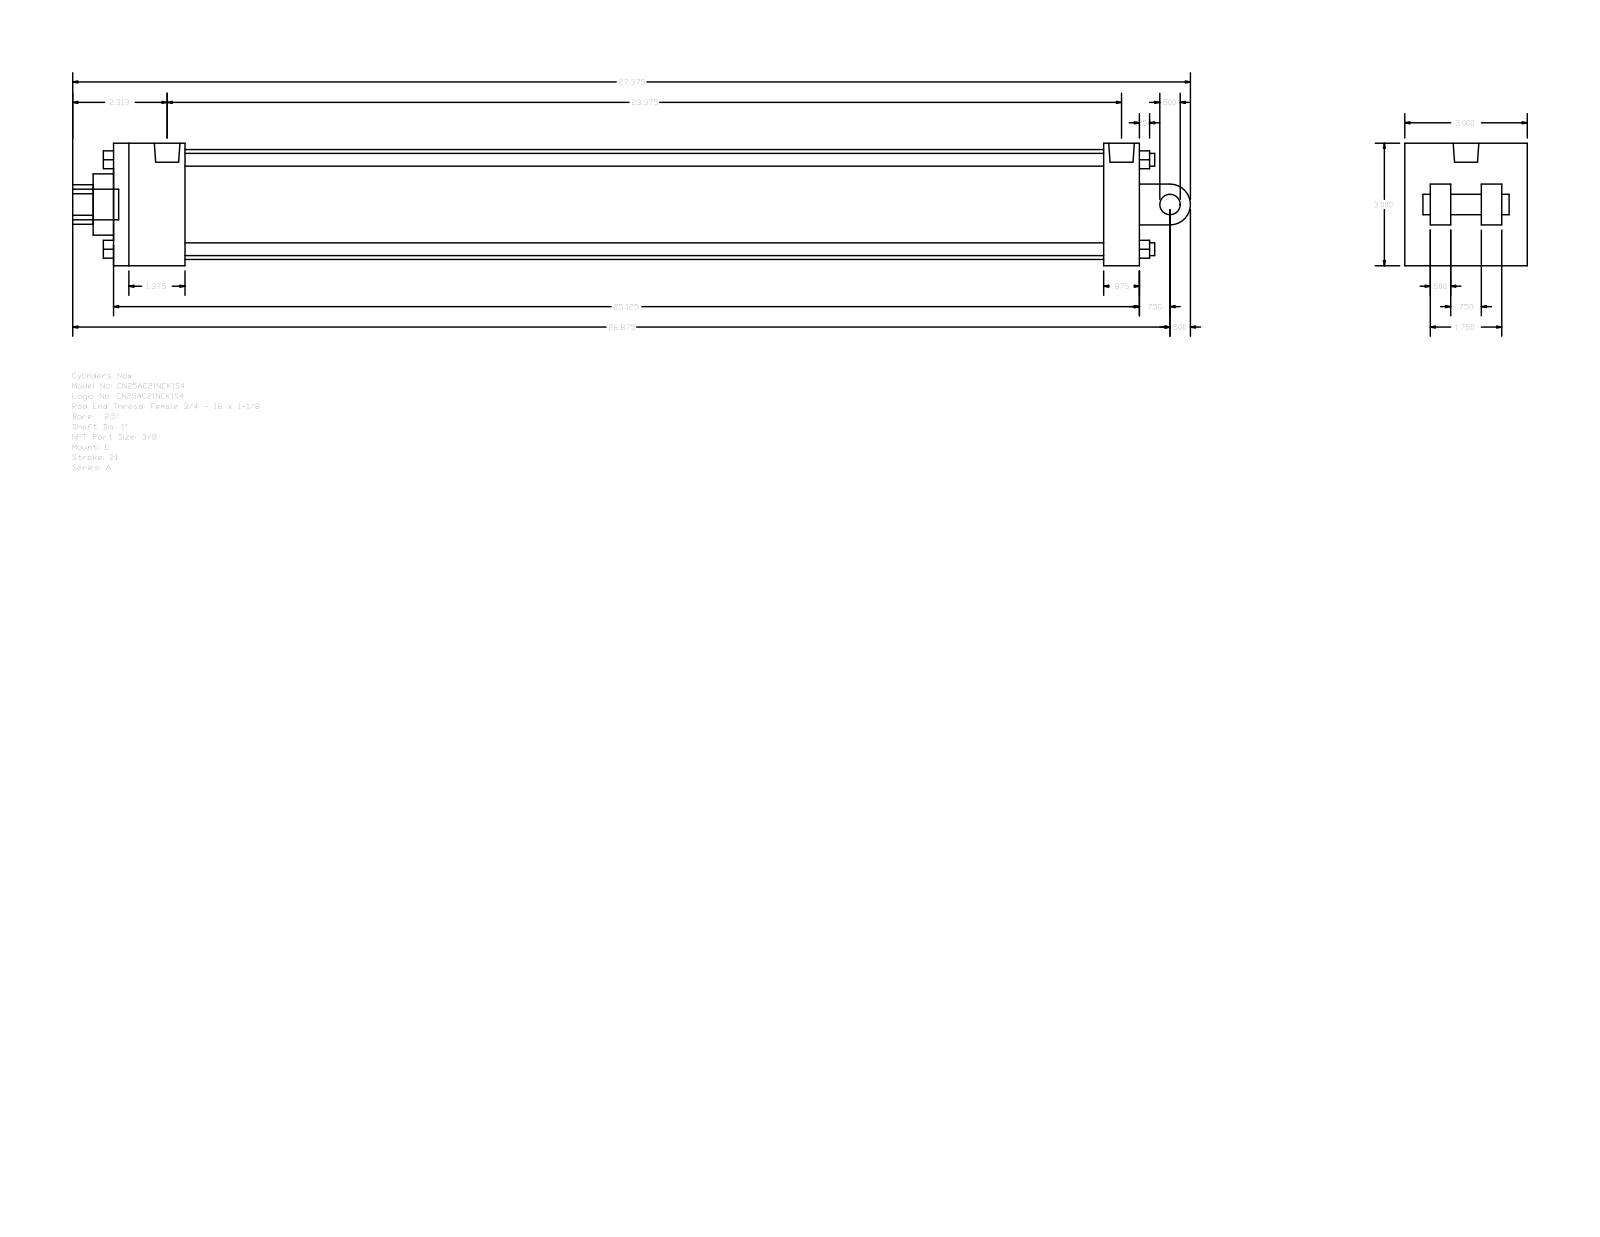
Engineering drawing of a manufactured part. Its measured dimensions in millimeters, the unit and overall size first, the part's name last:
Units: millimetres
Overall size (bounding box): 695.33 × 76.2 × 76.2
Round holes (diameter × count): ⌀5.56 ×2, ⌀15.93 ×1, ⌀25.4 ×1, ⌀38.1 ×1, ⌀68.33 ×1
Round bosses / shafts (diameter × count): ⌀7.94 ×4, ⌀5.56 ×2, ⌀19.05 ×1, ⌀15.93 ×1, ⌀12.7 ×1
Partial cylindrical surfaces — rounded edges, fillets, slot ends (radius × count): R12.29 ×1, R12.7 ×1
Main face-to-face distances: 76.2, 638.18, 12.7, 44.45, 615.95, 571.5, 593.73, 22.23, 15.87, 25.4
Hole centre spacings: 2.38
Bodies: 0 solids, 135 faces (102 planar, 33 cylindrical, 0 other)
Part name (STEP PRODUCT): A_C__0250_1
STEP written by: GSSL Pune (CONFIG_CONTROL_DESIGN)
